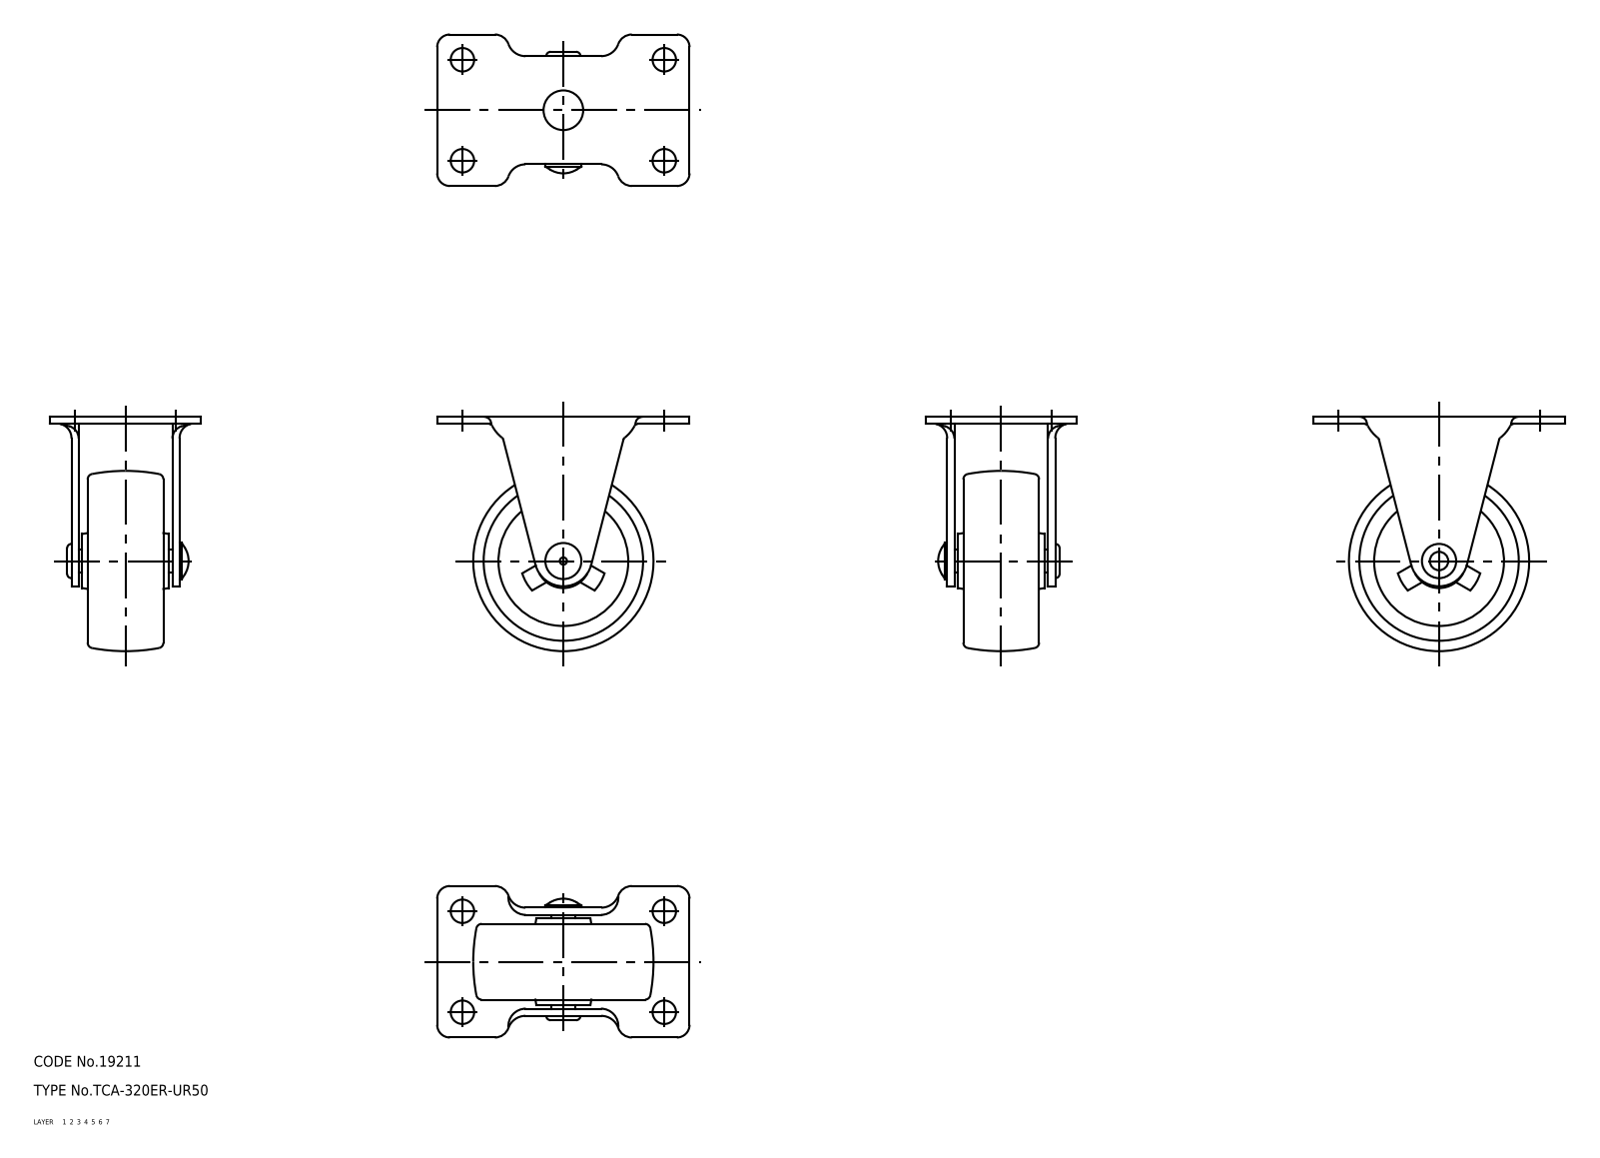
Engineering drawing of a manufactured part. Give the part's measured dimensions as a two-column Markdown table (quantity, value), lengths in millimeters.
| quantity | value |
| --- | --- |
| part name | wheel; axle; 320ER_UR50_3662_36 |
| STEP written by | CADfix (AUTOMOTIVE_DESIGN) |
| units | millimeters |
| bodies | 3 solids, 231 faces (0 planar, 0 cylindrical, 231 other) |
| overall size | 70 × 65 × 42 |
| volume | 41 420 mm³ |
| surface area | 19 324 mm² |
